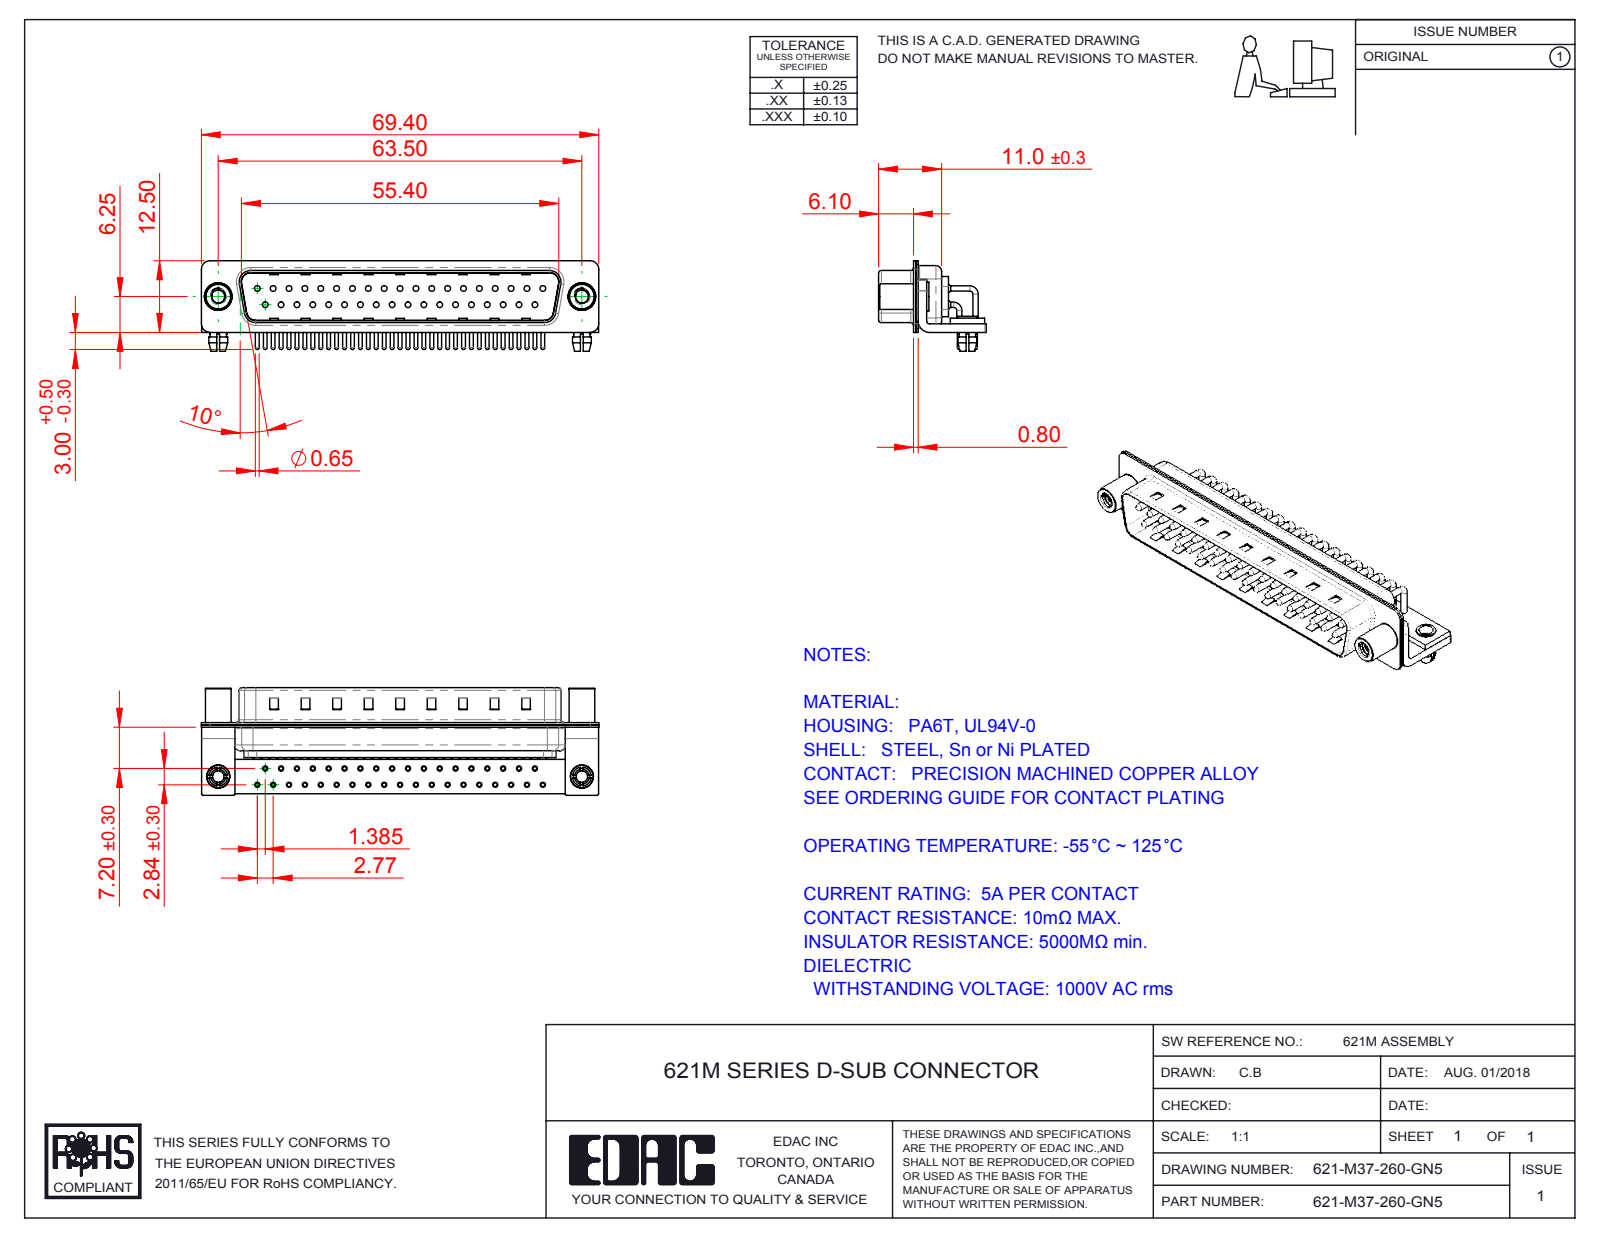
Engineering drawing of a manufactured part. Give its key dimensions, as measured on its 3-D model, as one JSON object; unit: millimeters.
{"part_name": "621M Contact Row 2; 621M Stabilizer Bracket; 621M 4-40 Threaded Standoff; 621M Shell Rear_37 Contacts (+6 more)", "step_written_by": "SolidWorks 2016 (CONFIG_CONTROL_DESIGN)", "units": "millimeters", "bodies": {"solids": 47, "faces": 4748, "planar": 2647, "cylindrical": 1643, "other": 458}, "overall_size": [69.4, 18.8, 15.8], "volume_mm3": 4770, "surface_area_mm2": 12476, "round_holes": [[2, 39], [0.9, 37], [1, 37], [1.7, 37], [2.26, 2], [2.5, 2], [3.2, 2], [4, 2], [4.8, 2]], "round_bosses_or_shafts": [[0.9, 46], [1.5, 37], [0.65, 37], [5, 2], [4.9, 2], [4.5, 2], [4, 2], [3.4, 2]], "partial_cylinders_radius": [[1.01, 37], [0.25, 16], [1.5, 16], [2, 13], [0.5, 9], [1.6, 8], [0.6, 4], [0.65, 4]], "face_to_face_distances": [0.4, 0.85, 1.25, 9.55, 1.5, 10.4, 8.3, 0.8, 8.7, 1], "hole_center_spacings": [3.16, 2.77, 5.54, 8.31, 11.08, 13.85, 5.03, 16.62]}
